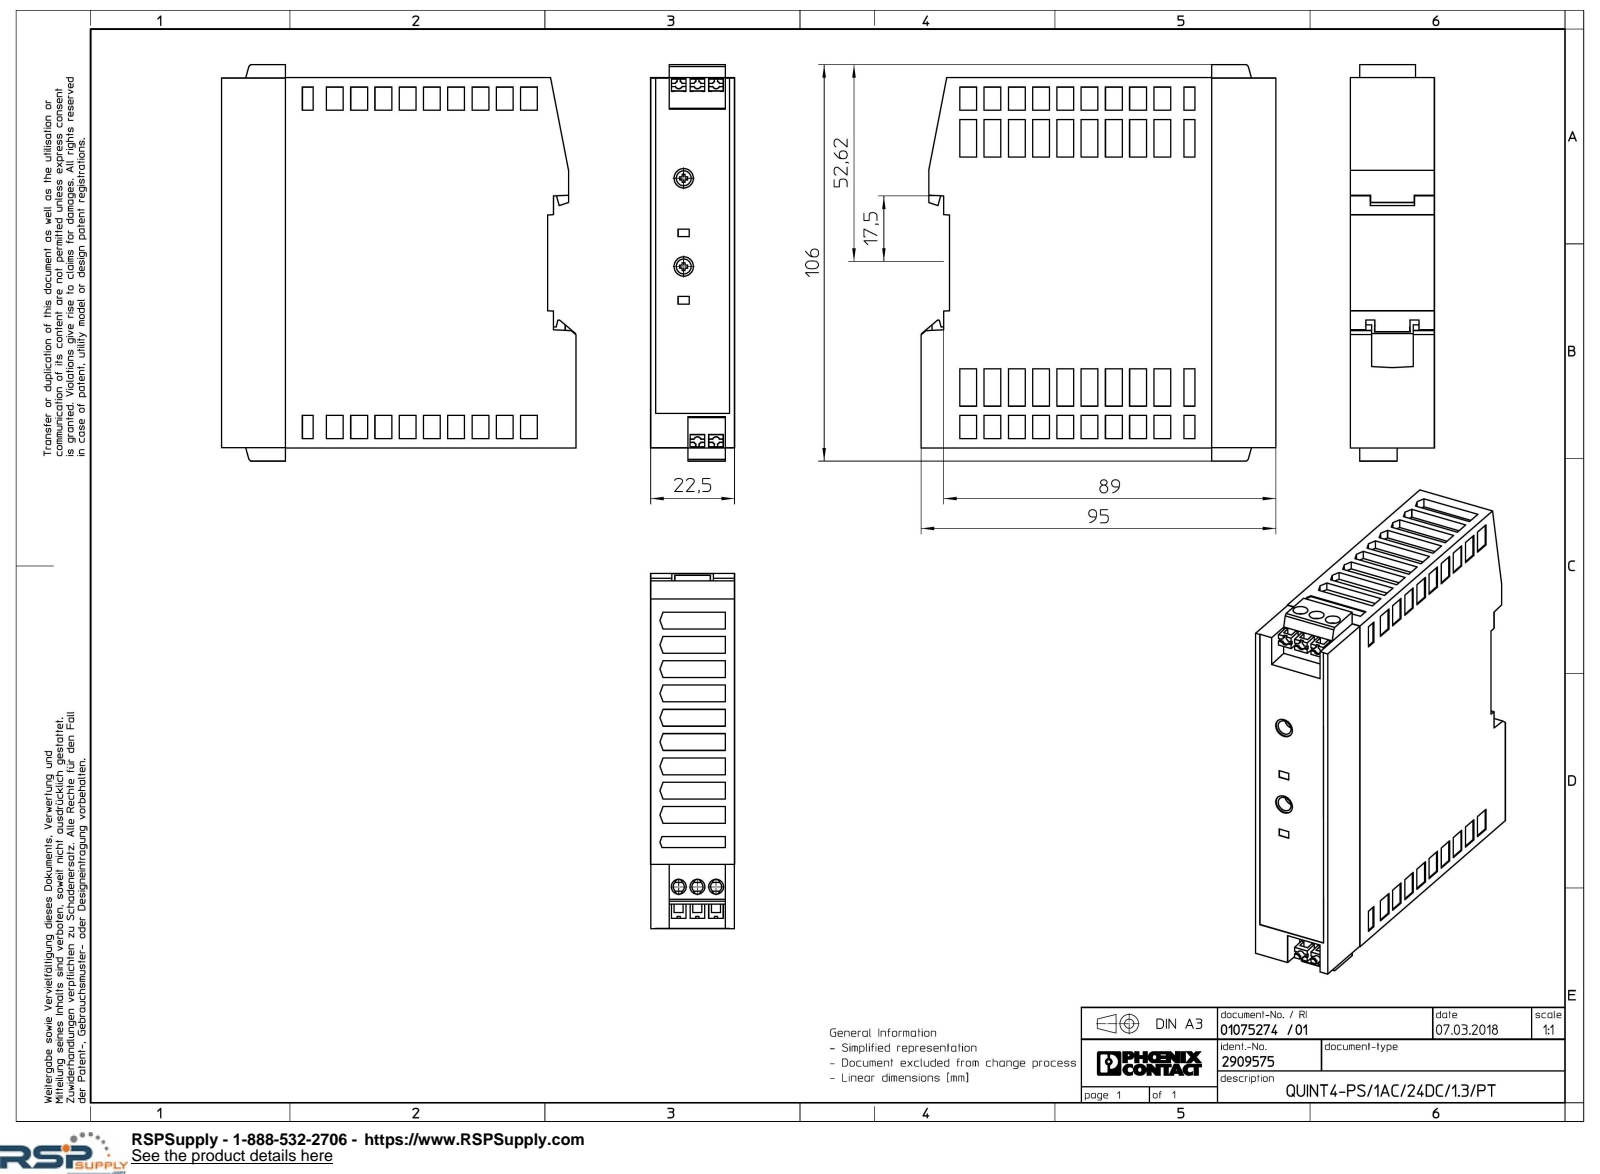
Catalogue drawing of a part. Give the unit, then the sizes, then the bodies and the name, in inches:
Units: inches
Overall size (bounding box): 4.173 × 3.74 × 0.886
Round holes (diameter × count): ⌀0.157 ×5, ⌀0.205 ×2
Partial cylindrical surfaces — rounded edges, fillets, slot ends (radius × count): R0.059 ×3
Main face-to-face distances: 0.886, 0.882, 0.875, 0.871, 0.878, 3.898, 0.256, 3.736, 0.079, 0.512
Hole centre spacings: 0.197, 0.394, 0.929
Volume: 12.09 in³ · Surface area: 47.29 in²
Bodies: 1 solid, 716 faces (663 planar, 28 cylindrical, 25 other)
Part name (STEP PRODUCT): QUINT4_PS_1AC_24DC_1.3_PT-select
STEP written by: Creo Elements/Direct Modeling 20.1A 29-Sep-2018 (C) Parametric Technology GmbH (AUTOMOTIVE_DESIGN)
